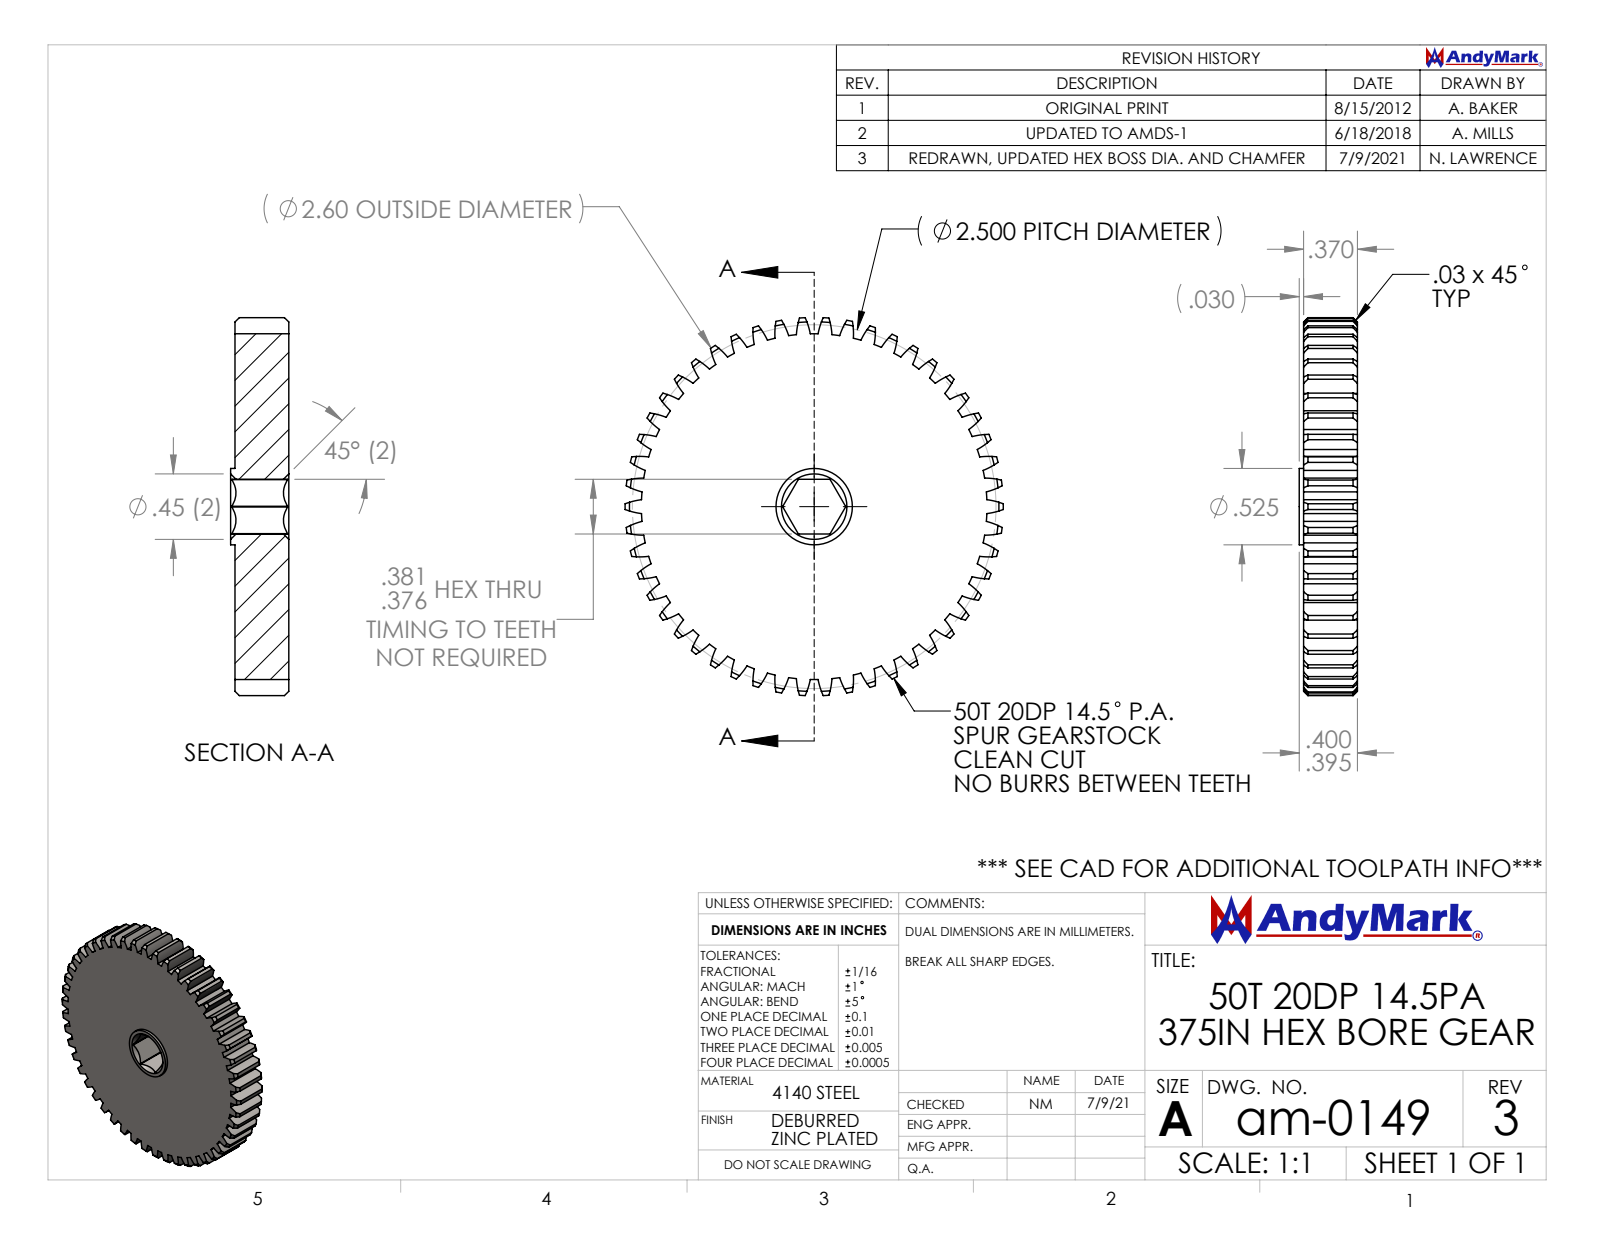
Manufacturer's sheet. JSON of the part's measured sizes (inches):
{"part_name": "am-0149 50T 20dp 375hex Gear REV3", "step_written_by": "SolidWorks 2021 (AUTOMOTIVE_DESIGN)", "units": "inches", "bodies": {"solids": 1, "faces": 318, "planar": 9, "cylindrical": 207, "other": 102}, "overall_size": [2.6, 2.597, 0.4], "volume_in3": 1.745, "surface_area_in2": 15.85, "round_bosses_or_shafts": [[0.525, 1]], "partial_cylinders_radius": [[0.5, 100], [0.005, 6], [1.188, 1], [1.3, 1]], "face_to_face_distances": [0.37, 0.376, 0.4, 0.03]}
